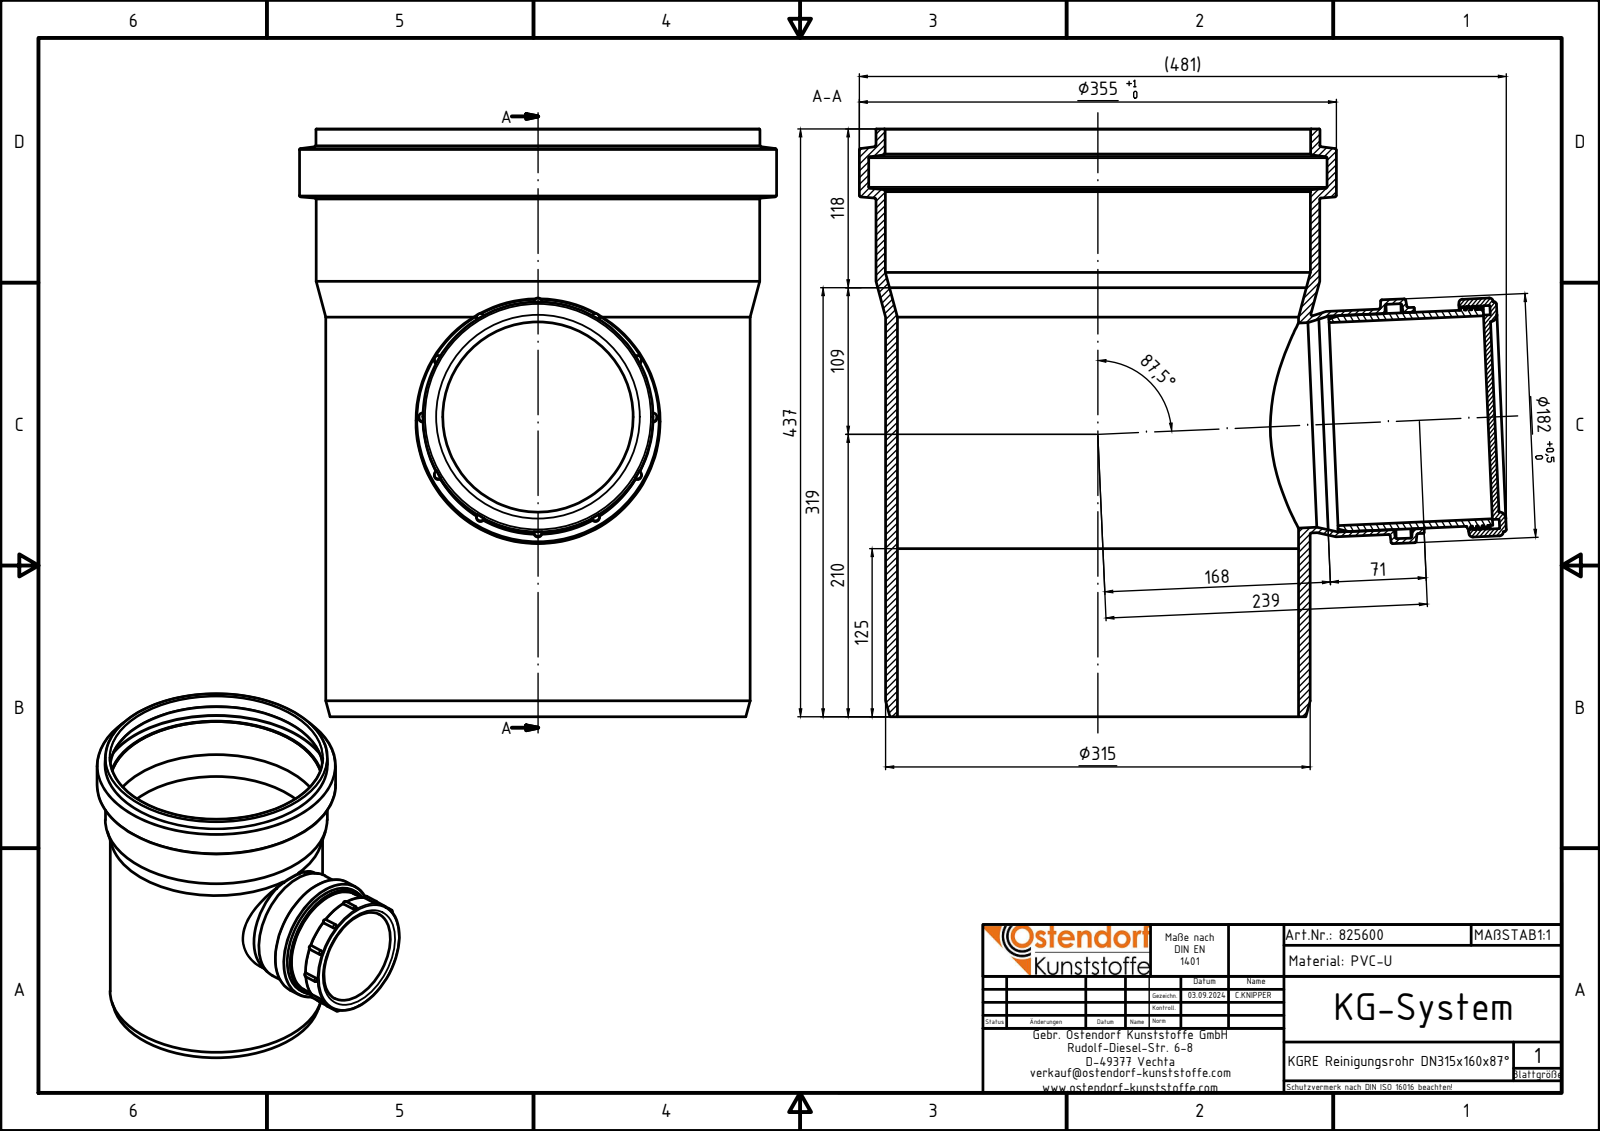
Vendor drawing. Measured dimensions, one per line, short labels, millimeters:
name: 825600z; 825600z Deckel; 825600z Einsatz
written by: Autodesk Inventor 2024 (AUTOMOTIVE_DESIGN)
unit: mm
bodies: 3 solids, 157 faces (13 planar, 49 cylindrical, 95 other)
size: 481.06 × 437 × 354.7
volume: 4 152 000 mm³; area: 1 196 000 mm²
holes: 2× ⌀161.1, 1× ⌀151, 1× ⌀152.3, 1× ⌀160.7, 1× ⌀162.3, 1× ⌀166, 1× ⌀174.4, 1× ⌀298.2, 1× ⌀316, 1× ⌀316.3, 1× ⌀340.9
bosses: 1× ⌀354.7, 1× ⌀330.1, 1× ⌀329.8, 1× ⌀315.6, 1× ⌀181.4, 1× ⌀171, 1× ⌀168.1, 1× ⌀167.7
rounds: 12× R3
face distances: 4.97, 437, 10, 5.03, 5.01, 4.99, 5.02, 5.06, 10.05, 115
